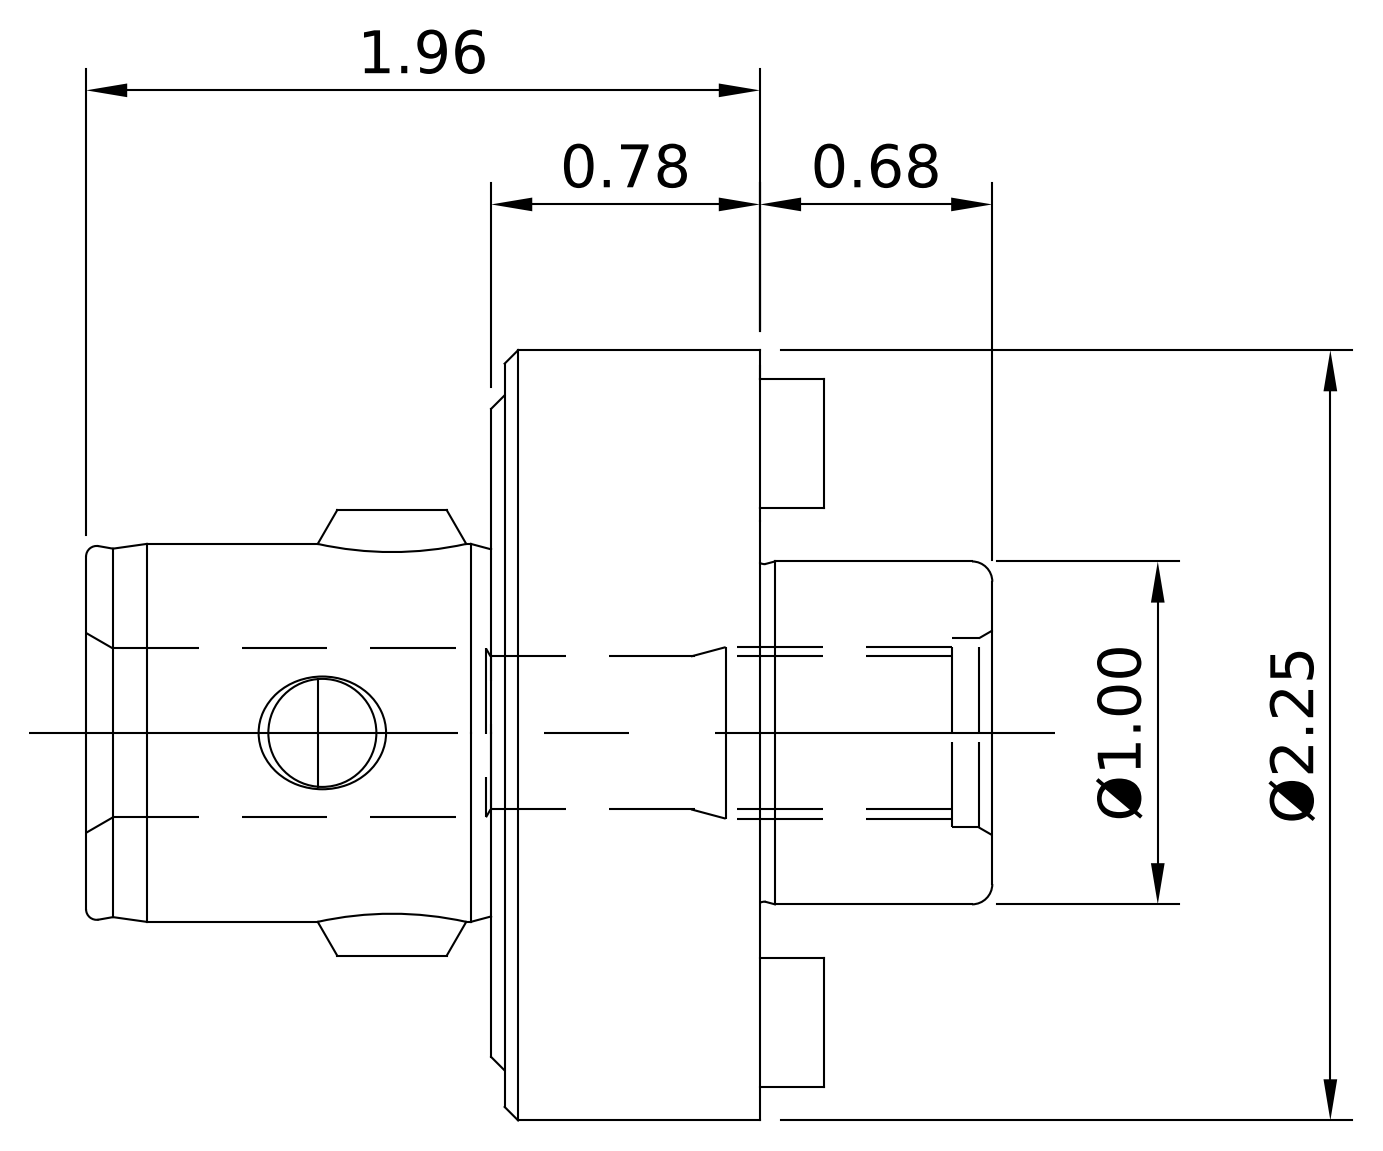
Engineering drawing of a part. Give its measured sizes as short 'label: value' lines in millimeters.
name: 11.690.711; 11.335.456; 11.691.622; 10.691.50X_10.691.505
written by: SolidWorks 2016 (AUTOMOTIVE_DESIGN)
unit: mm
bodies: 5 solids, 261 faces (53 planar, 80 cylindrical, 128 other)
size: 77.03 × 57.2 × 57.2
volume: 79 810 mm³; area: 21 882 mm²
holes: 2× ⌀9.5, 1× ⌀8, 1× ⌀8.03, 1× ⌀11, 1× ⌀11.51, 1× ⌀12.5, 1× ⌀14.5
bosses: 2× ⌀9.53, 2× ⌀9.51, 1× ⌀57.2, 1× ⌀29.97, 1× ⌀28, 1× ⌀25.4, 1× ⌀12.7, 1× ⌀10.9
rounds: 1× R14
face distances: 20, 37.5, 17.5, 47.03, 27.03, 9.53, 1, 19, 36.5, 46.03
hole spacings: 21.43, 42.86
